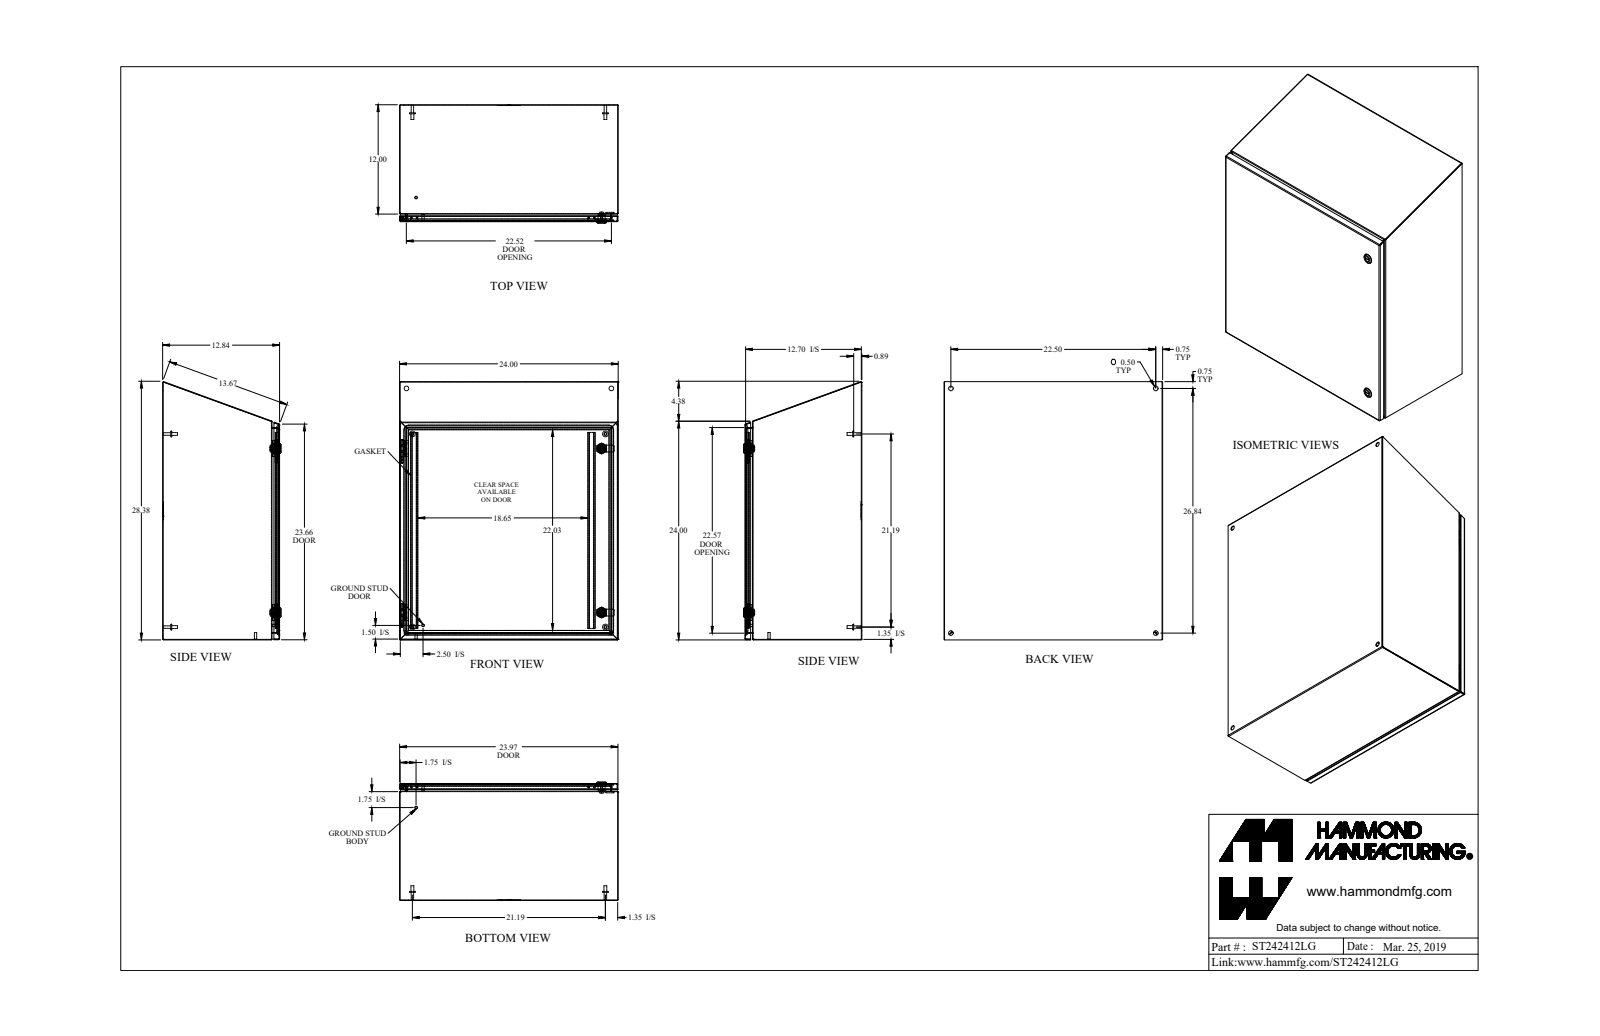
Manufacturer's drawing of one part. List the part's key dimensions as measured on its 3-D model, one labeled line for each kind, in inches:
Part name (STEP PRODUCT): ST242412LG
STEP written by: SolidWorks 2018 (AUTOMOTIVE_DESIGN)
Units: inches
Bodies: 29 solids, 766 faces (394 planar, 248 cylindrical, 124 other)
Overall size (bounding box): 28.342 × 24 × 12.997
Volume: 173.5 in³ · Surface area: 5 700 in²
Round holes (diameter × count): ⌀0.5 ×4, ⌀0.232 ×2, ⌀0.625 ×2, ⌀0.785 ×2, ⌀0.172 ×1, ⌀0.24 ×1, ⌀0.242 ×1
Round bosses / shafts (diameter × count): ⌀0.625 ×4, ⌀0.313 ×4, ⌀0.27 ×4, ⌀1.1 ×2, ⌀0.525 ×2, ⌀0.281 ×2, ⌀0.25 ×2, ⌀0.455 ×1
Partial cylindrical surfaces — rounded edges, fillets, slot ends (radius × count): R0.029 ×15, R0.086 ×15, R0.188 ×13, R0.043 ×12, R0.081 ×12, R0.006 ×4, R0.036 ×4, R0.062 ×4
Main face-to-face distances: 0.057, 12.765, 12.708, 23.943, 0.072, 12.837, 12.78, 23.886, 24, 11.943
Hole centre spacings: 22.5, 26.842, 35.025, 2.494, 6.678, 18, 20.279, 21.544
